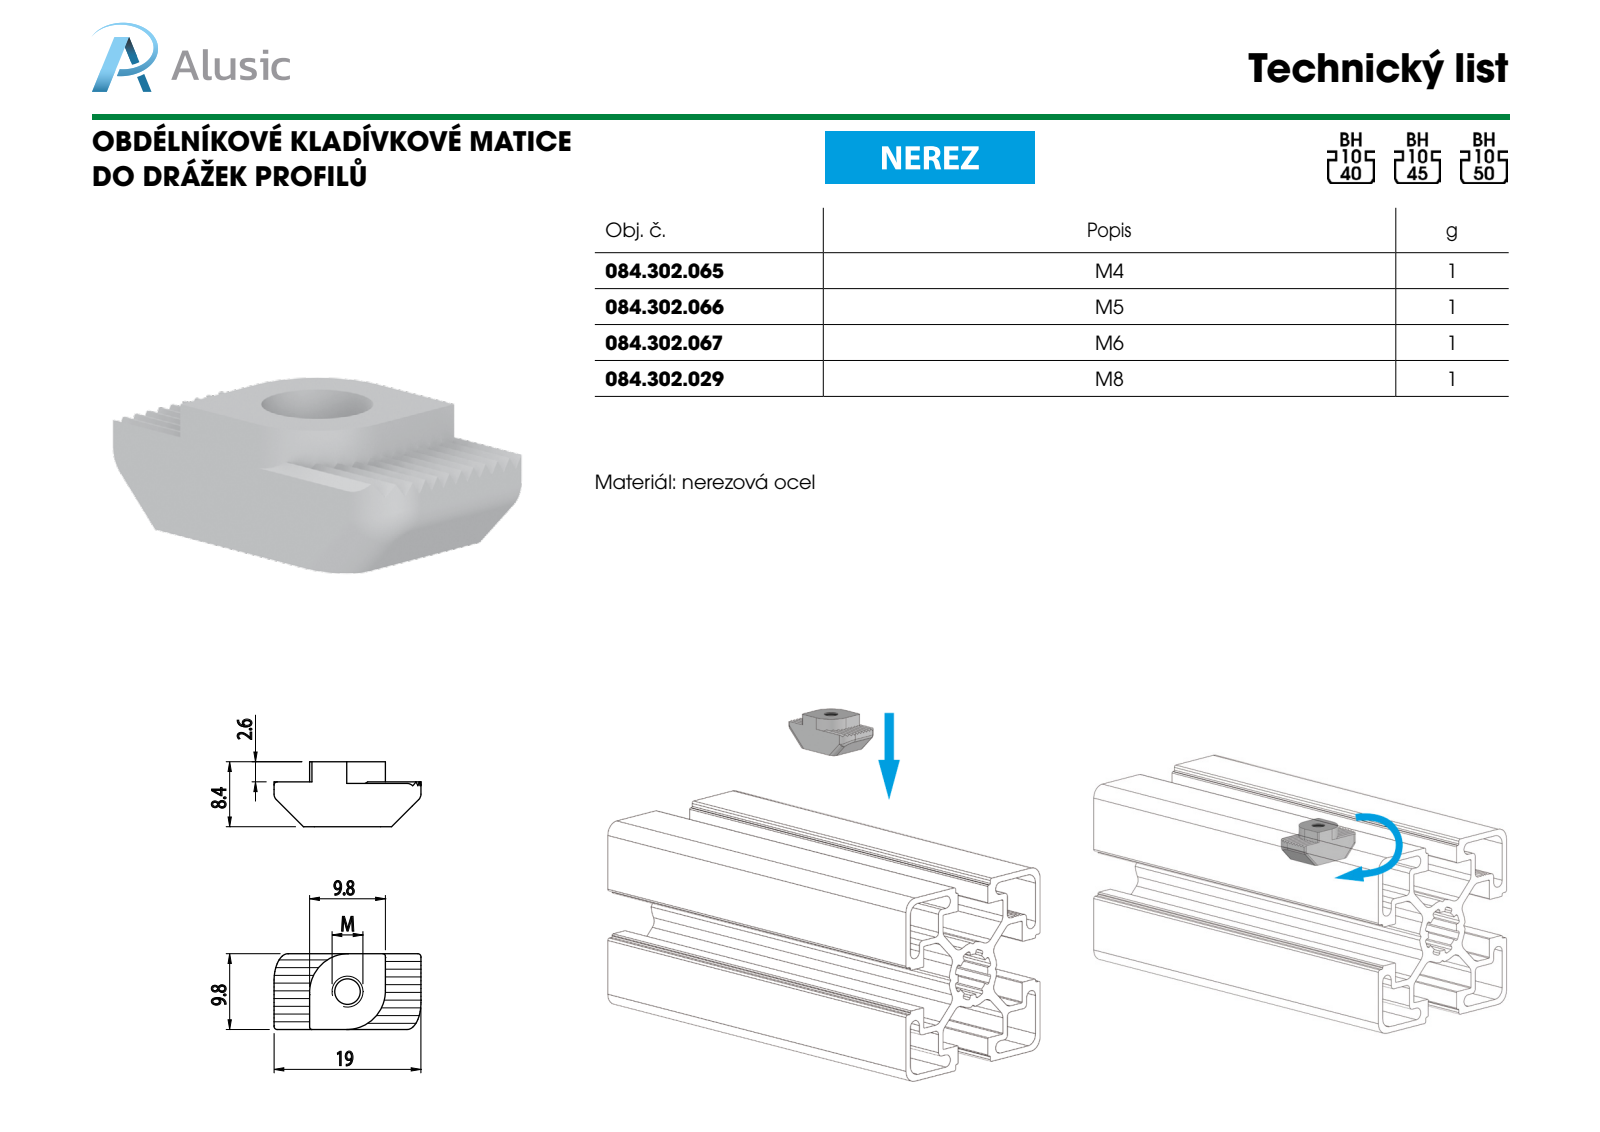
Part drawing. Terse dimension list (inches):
name: 084.302.029
written by: SolidWorks 2016 (CONFIG_CONTROL_DESIGN)
unit: in
bodies: 1 solid, 166 faces (142 planar, 24 cylindrical, 0 other)
size: 0.748 × 0.386 × 0.339
volume: 0.05 in³; area: 1.51 in²
holes: 1× ⌀0.268
rounds: 2× R0.118, 2× R0.197
face distances: 0.386, 0.018, 0.255, 0.021, 0.036, 0.339, 0.273, 0.039, 0.237, 0.276
